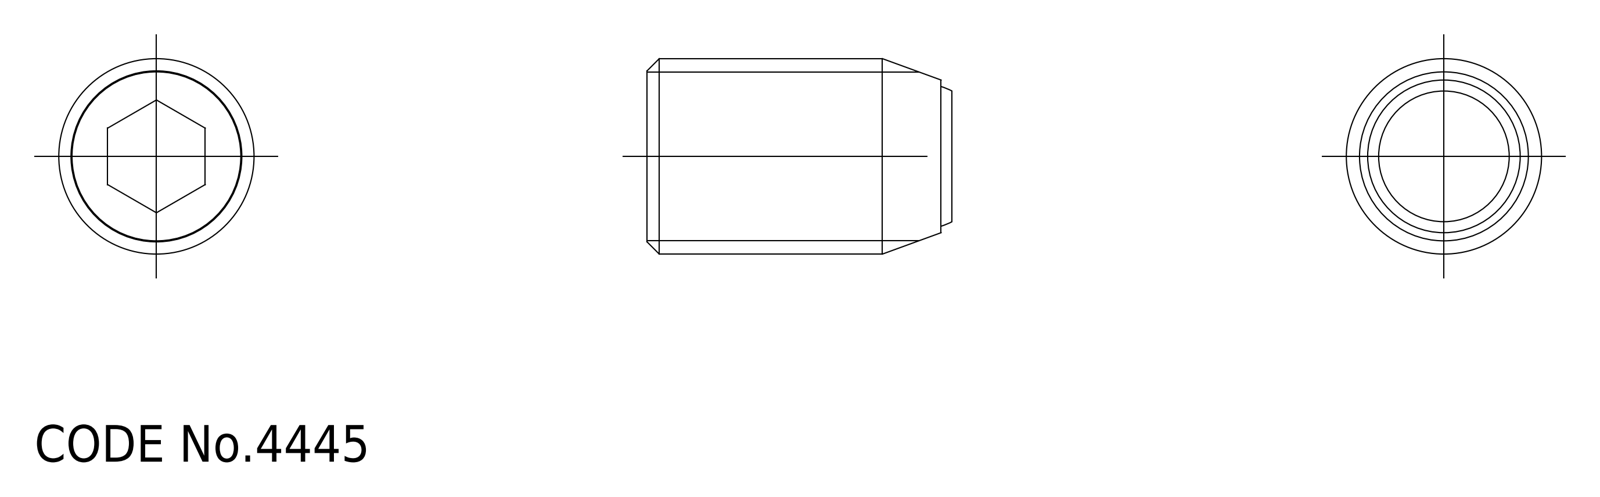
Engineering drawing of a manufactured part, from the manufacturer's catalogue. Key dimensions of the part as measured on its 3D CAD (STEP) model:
Part name (STEP PRODUCT): ball; SCS_M16_25_F_16565_36
STEP written by: CADfix (AUTOMOTIVE_DESIGN)
Units: millimetres
Bodies: 2 solids, 20 faces (0 planar, 0 cylindrical, 20 other)
Overall size (bounding box): 26.38 × 16 × 16
Volume: 3 716 mm³ · Surface area: 2 569 mm²
